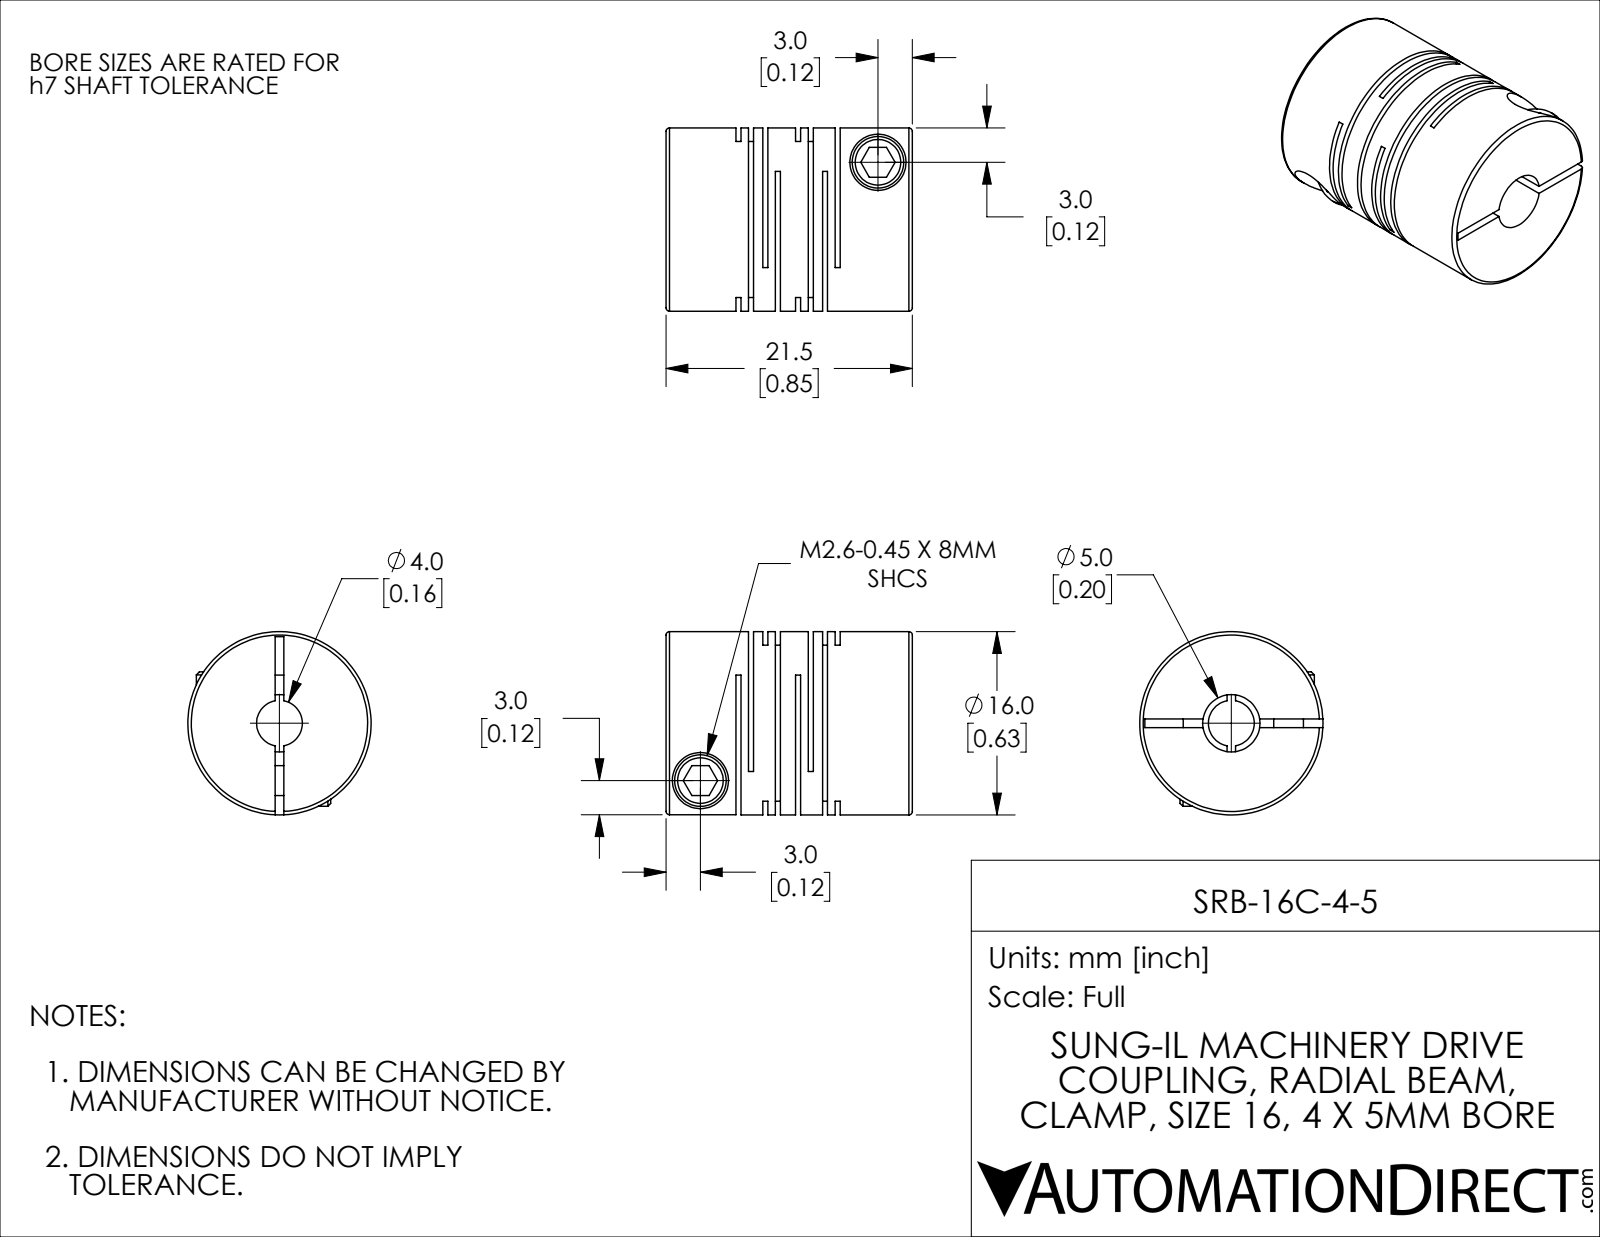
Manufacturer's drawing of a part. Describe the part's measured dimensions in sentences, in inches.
The part is named "SRB-16C-4-5". Its 3-D file was written by "SolidWorks 2021 (CONFIG_CONTROL_DESIGN)". It is 1 solid with 114 faces: 60 planar, 42 cylindrical and 12 other. Overall it measures 0.846 by 0.63 by 0.63 inches. Its volume is 0.198 cubic inches and its surface area 6.774 square inches. Round holes: 2 of diameter 0.102, 2 of diameter 0.193, 1 of diameter 0.157, 1 of diameter 0.197. Round bosses or shafts: 2 of diameter 0.177, 1 of diameter 0.63. The main face-to-face distances are 0.043, 0.093, 0.017, 0.205, 0.026, 0.075, 0.188, 0.049, 0.162, 0.113.
